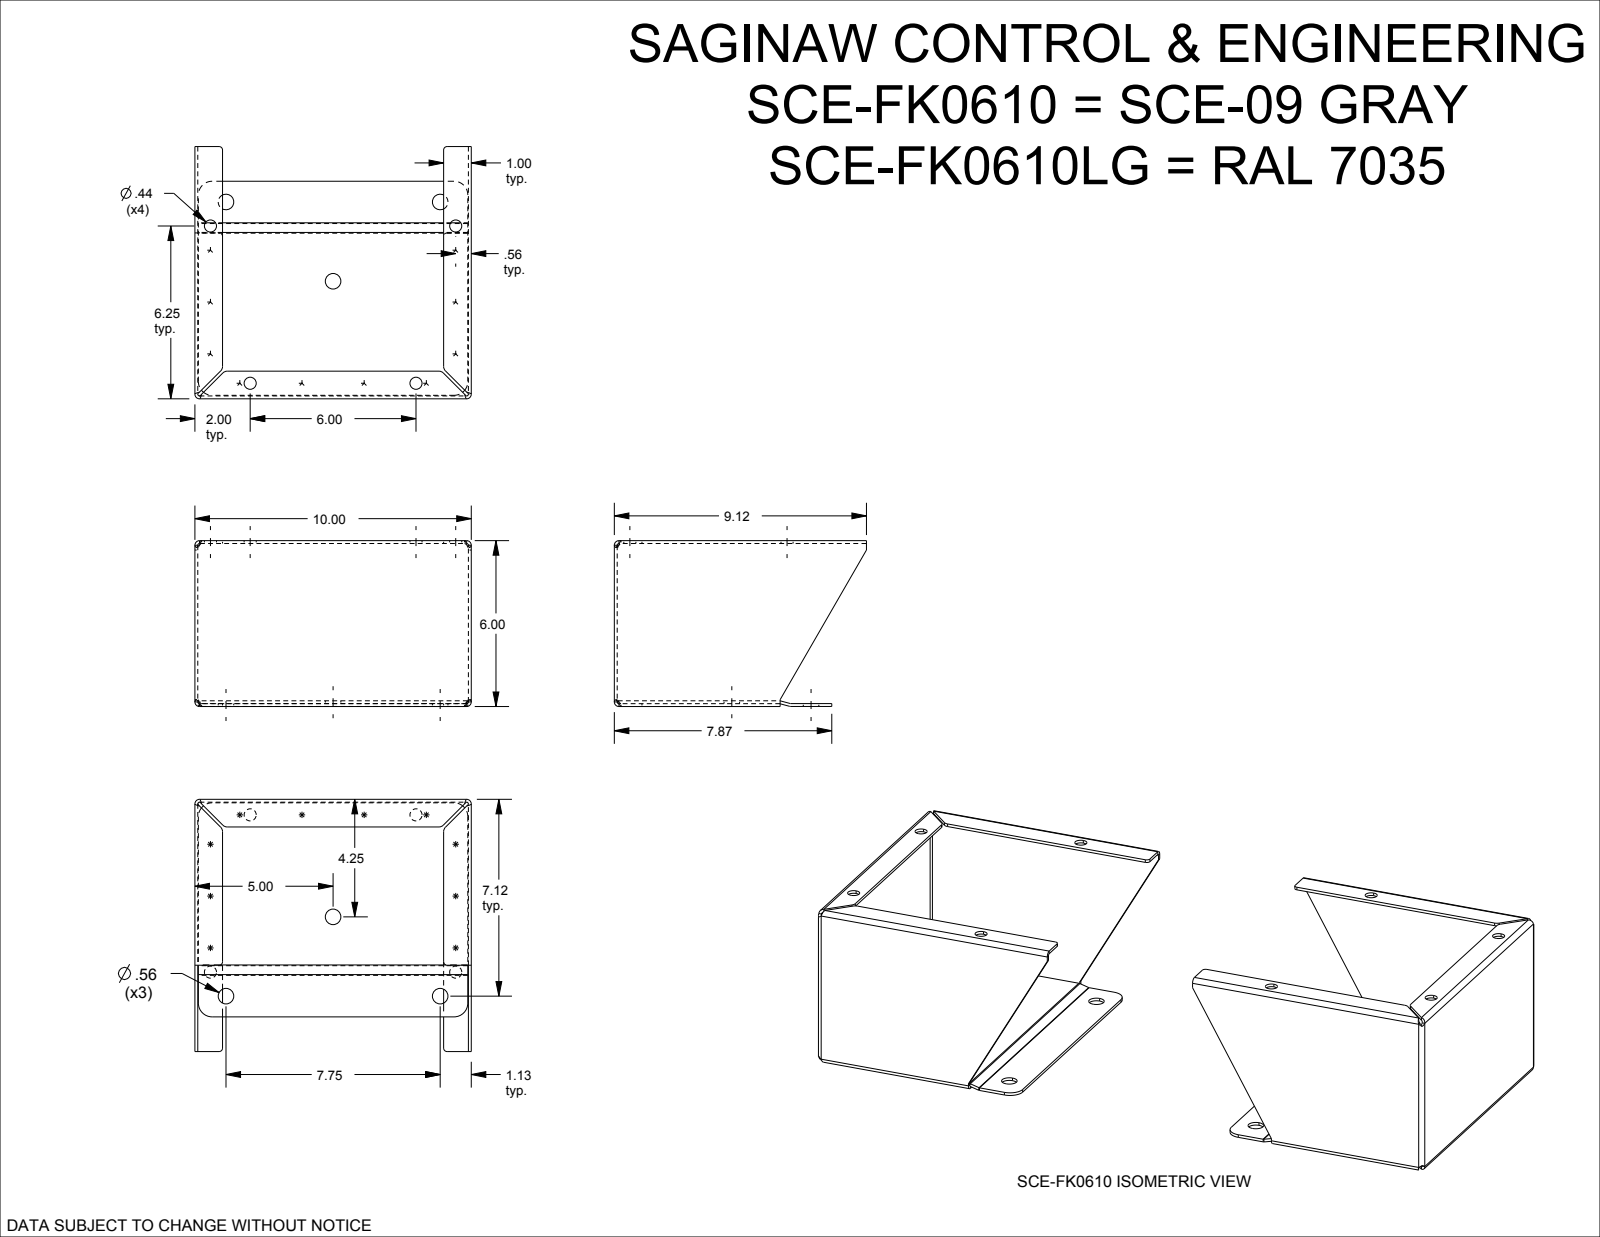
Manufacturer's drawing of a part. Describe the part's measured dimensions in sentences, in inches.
The part is named "SCE-FK0610". Its 3-D file was written by "SolidWorks 2019 (CONFIG_CONTROL_DESIGN)". It is 4 solids with 214 faces: 96 planar, 86 cylindrical and 32 other. Overall it measures 24 by 10 by 6 inches. Its volume is 54.32 cubic inches and its surface area 1 069 square inches. Round holes: 8 of diameter 0.437, 6 of diameter 0.563. Partial cylindrical surfaces (rounded edges, fillets, slot ends): 16 of radius 0.166, 10 of radius 0.062, 10 of radius 0.063, 8 of radius 0.125, 8 of radius 0.22, 8 of radius 0.5. The main face-to-face distances are 0.104, 9.896, 23.896, 9.792, 10, 5.792, 5.896, 0.101, 5.893, 24. The hole center spacings are 1.035, 4.755, 4.867, 5.866, 6.614, 9.363, 10.646, 13.211.
